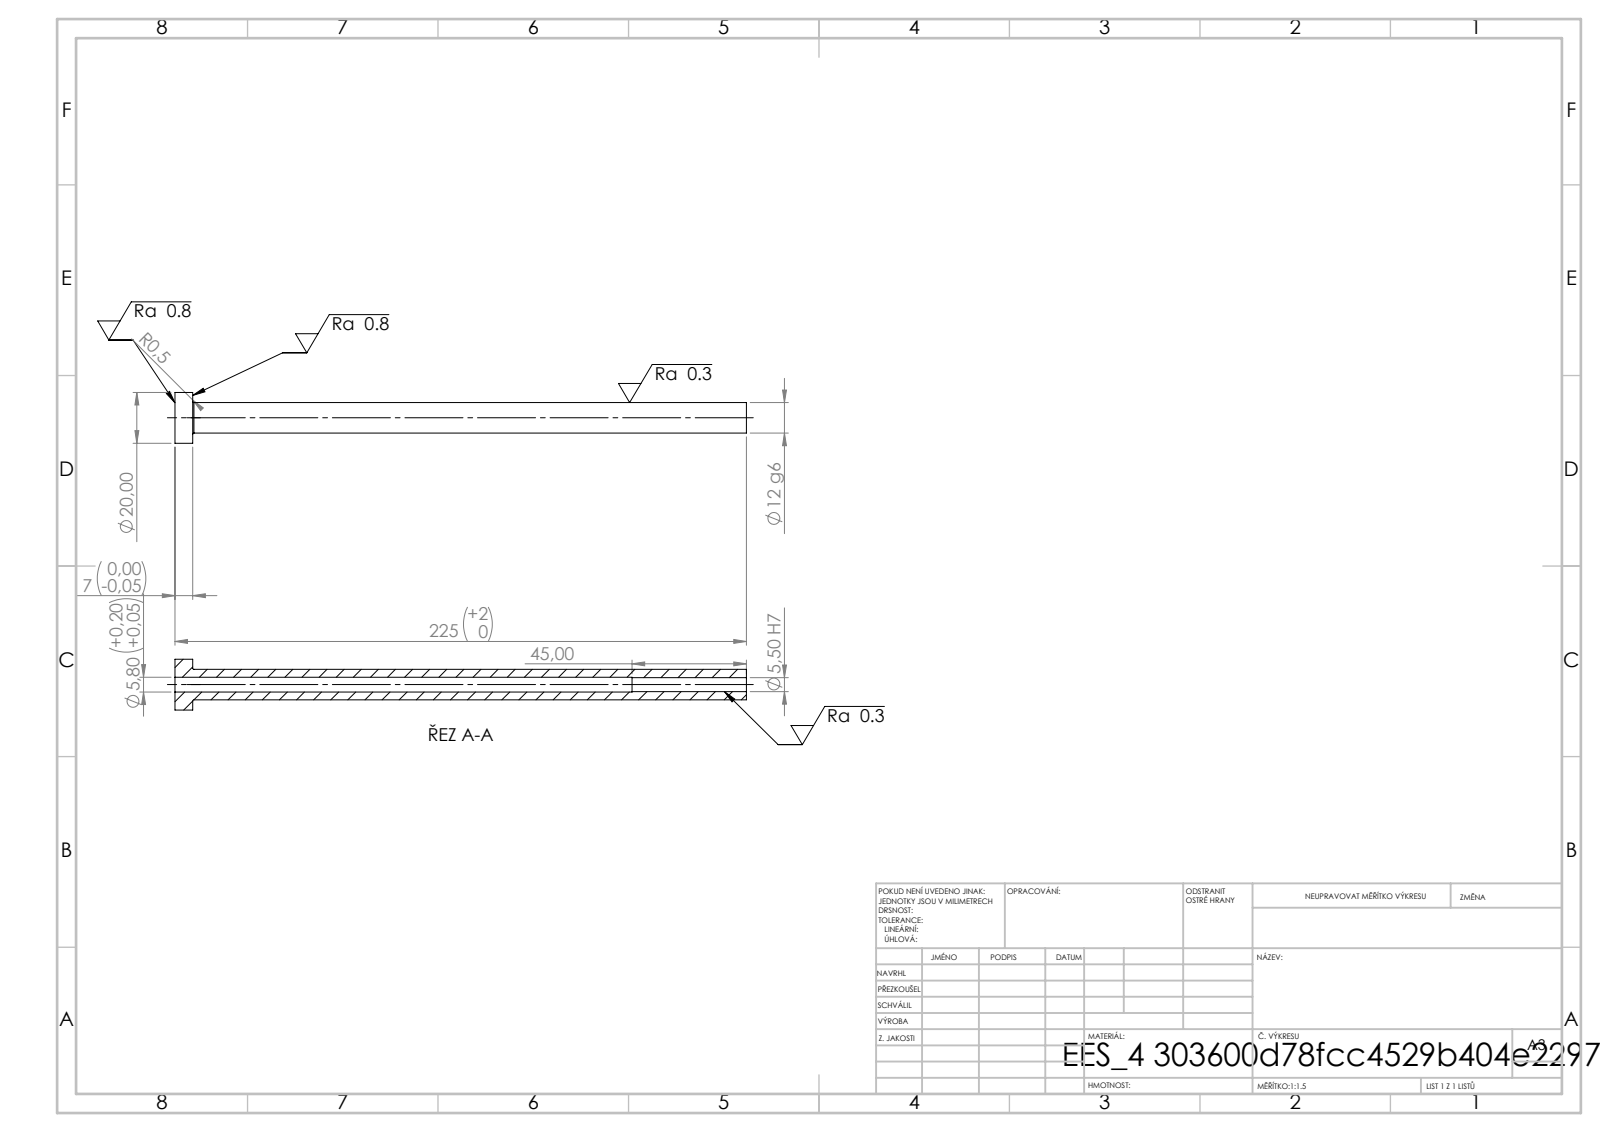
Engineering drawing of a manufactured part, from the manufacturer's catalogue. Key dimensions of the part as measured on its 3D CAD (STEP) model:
STEP written by: SolidWorks 2019 (CONFIG_CONTROL_DESIGN)
Units: millimetres
Bodies: 1 solid, 14 faces (4 planar, 8 cylindrical, 2 other)
Overall size (bounding box): 225 × 20 × 20
Volume: 21 032 mm³ · Surface area: 13 288 mm²
Round holes (diameter × count): ⌀5.5 ×1, ⌀5.8 ×1
Round bosses / shafts (diameter × count): ⌀20 ×1, ⌀12 ×1
Main face-to-face distances: 7, 225, 218, 180, 173, 45
